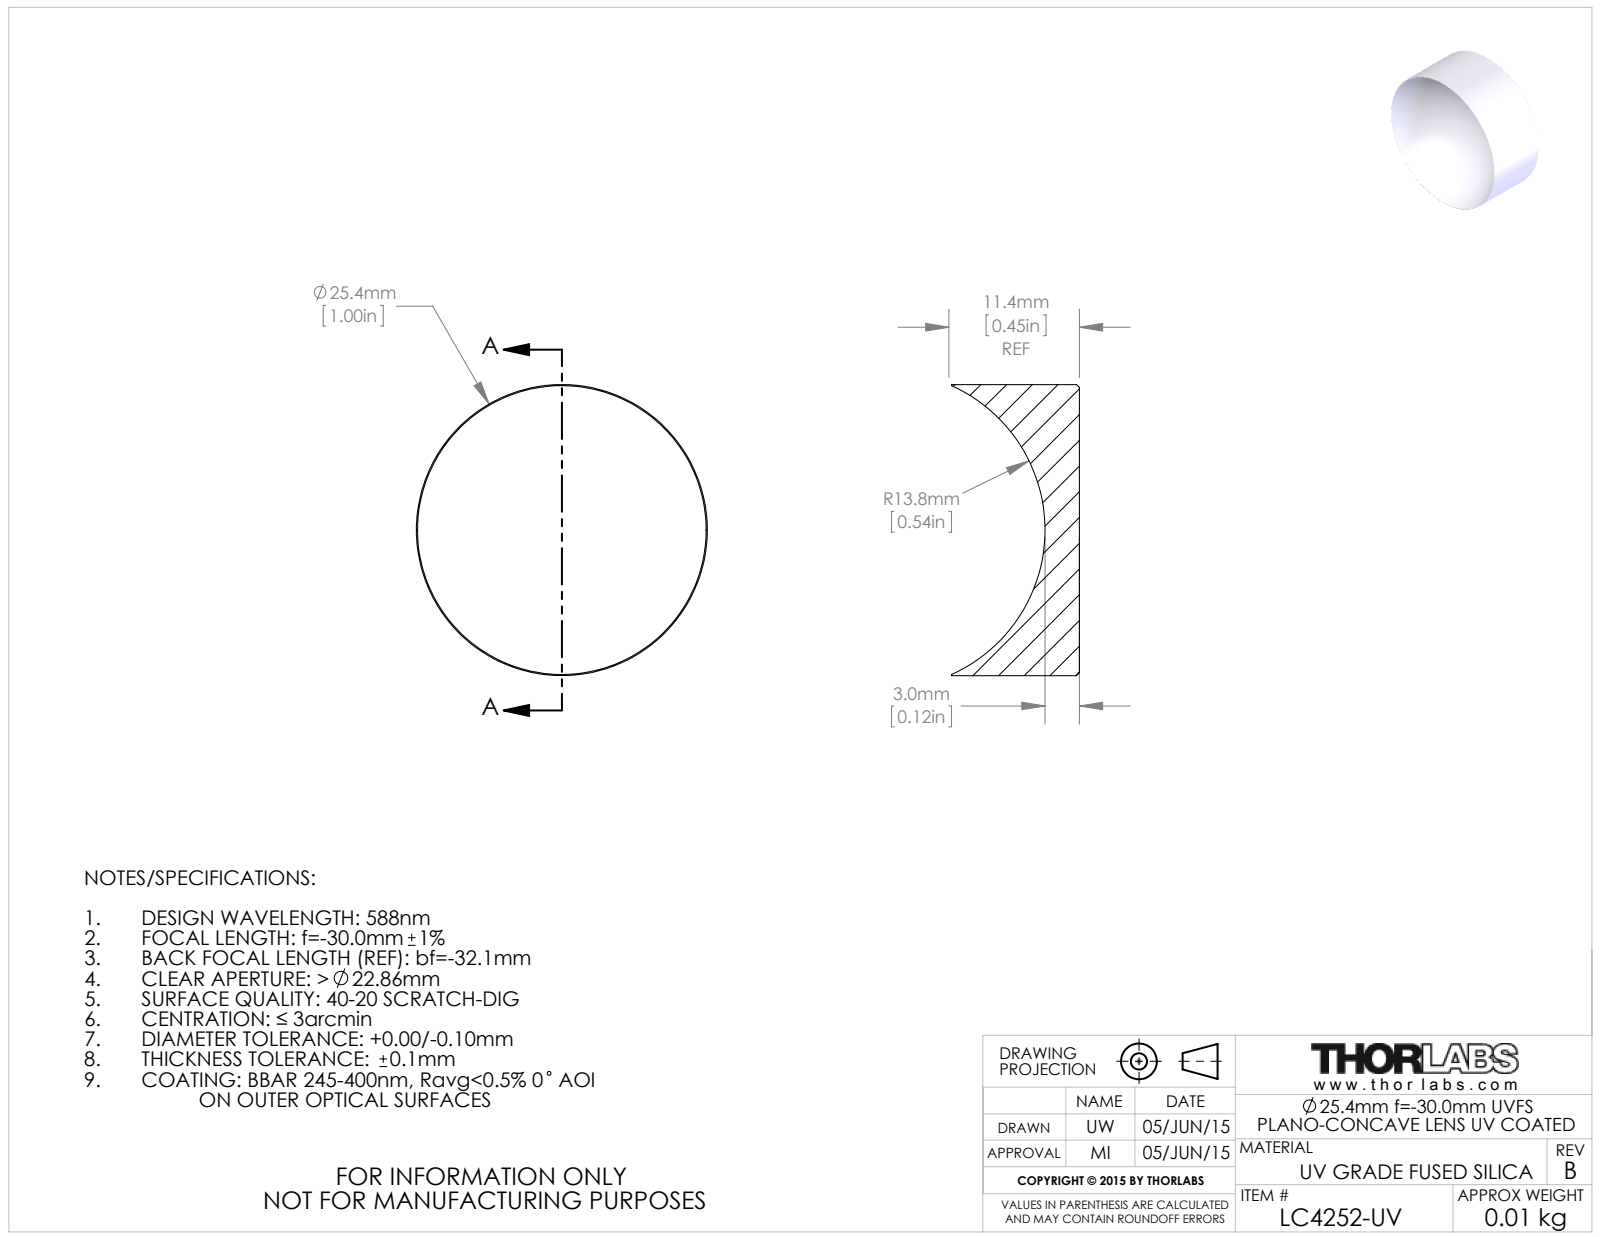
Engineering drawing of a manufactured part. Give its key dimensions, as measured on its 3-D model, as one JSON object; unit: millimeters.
{"part_name": "4350-E0W", "step_written_by": "SolidWorks 2014 (CONFIG_CONTROL_DESIGN)", "units": "millimeters", "bodies": {"solids": 1, "faces": 9, "planar": 1, "cylindrical": 2, "other": 6}, "overall_size": [25.4, 25.4, 11.17], "volume_mm3": 3335, "surface_area_mm2": 2101, "round_bosses_or_shafts": [[25.4, 1]]}
